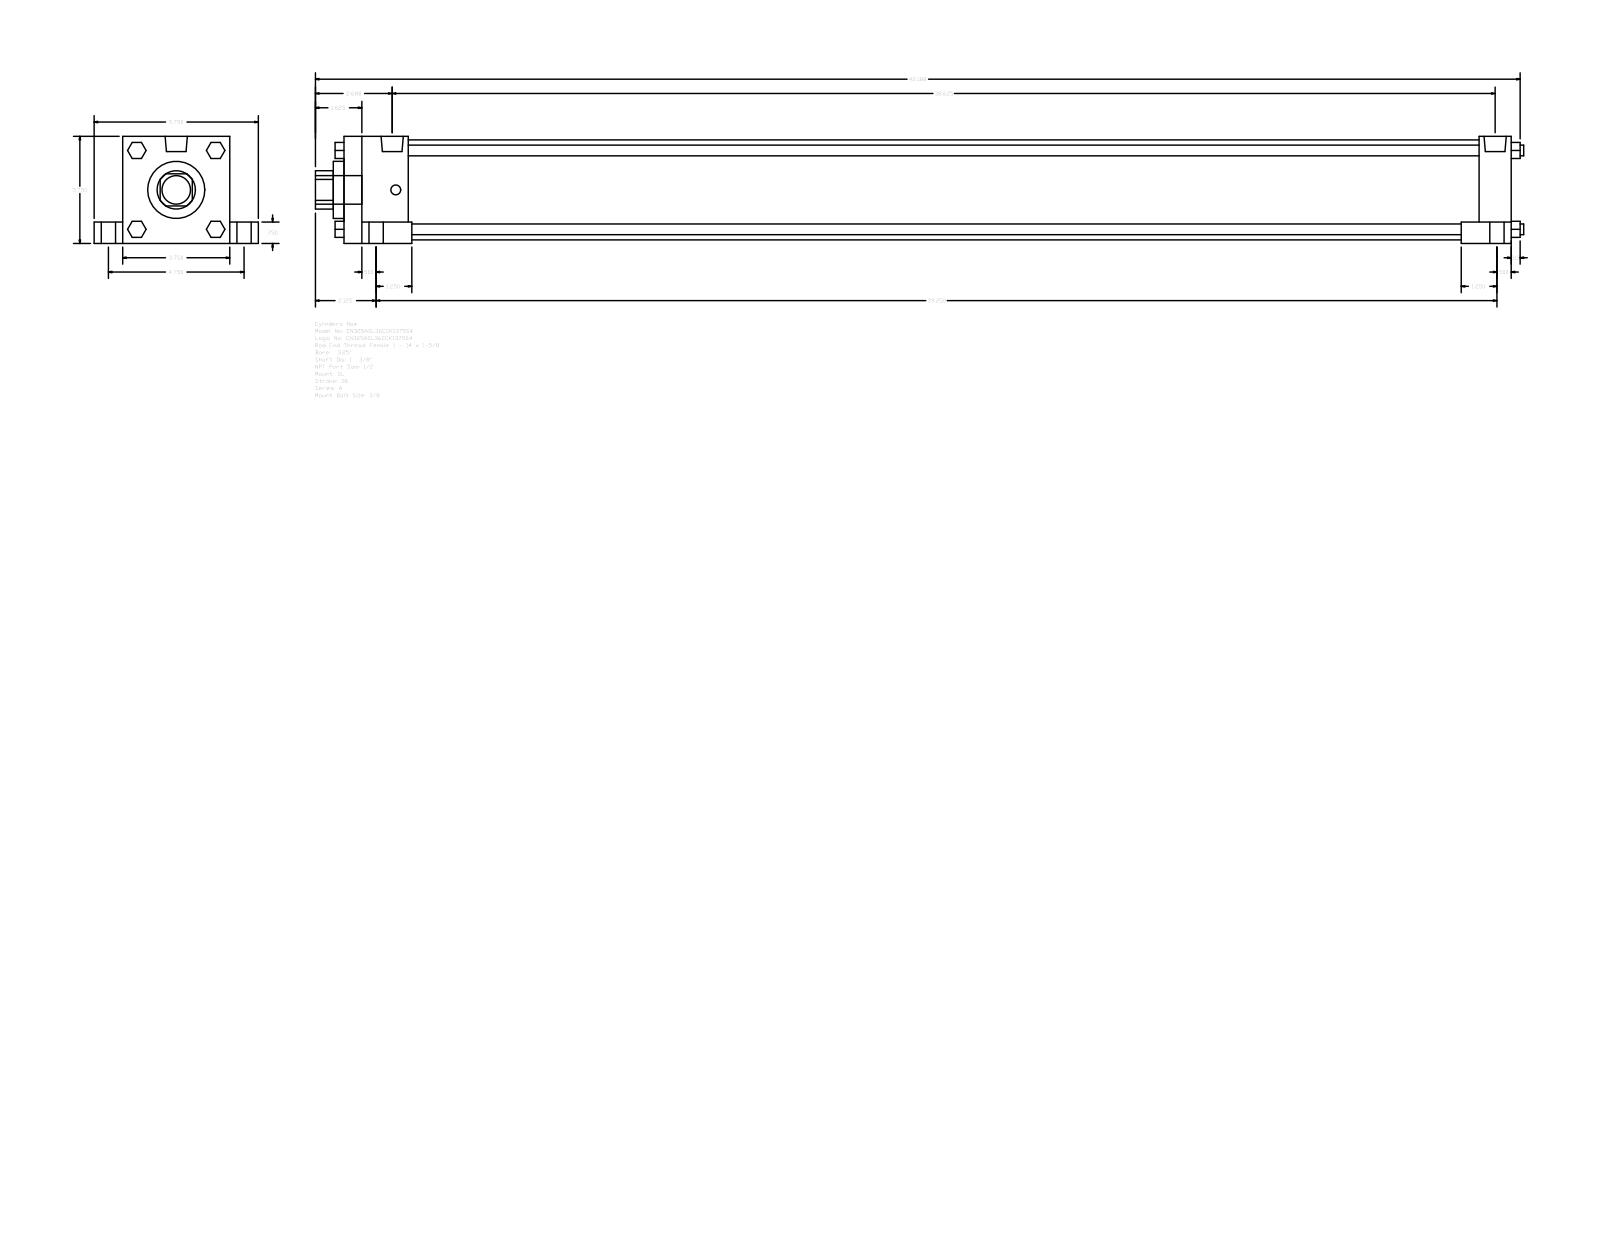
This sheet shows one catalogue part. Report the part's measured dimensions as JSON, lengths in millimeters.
{"part_name": "A_SL__0325_1.375", "step_written_by": "GSSL Pune (CONFIG_CONTROL_DESIGN)", "units": "millimeters", "bodies": {"solids": 0, "faces": 150, "planar": 114, "cylindrical": 36, "other": 0}, "overall_size": [1074.74, 146.05, 95.25], "round_holes": [[34.92, 1], [50.8, 1], [88.9, 1]], "round_bosses_or_shafts": [[19.05, 4], [12.7, 4], [9.53, 4], [8.73, 4], [19.77, 2], [25.4, 1]], "partial_cylinders_radius": [[17.06, 1]], "face_to_face_distances": [95.24, 1038.22, 25.41, 120.65, 19.05, 76.19, 28.57, 57.15, 1009.65, 952.5]}
